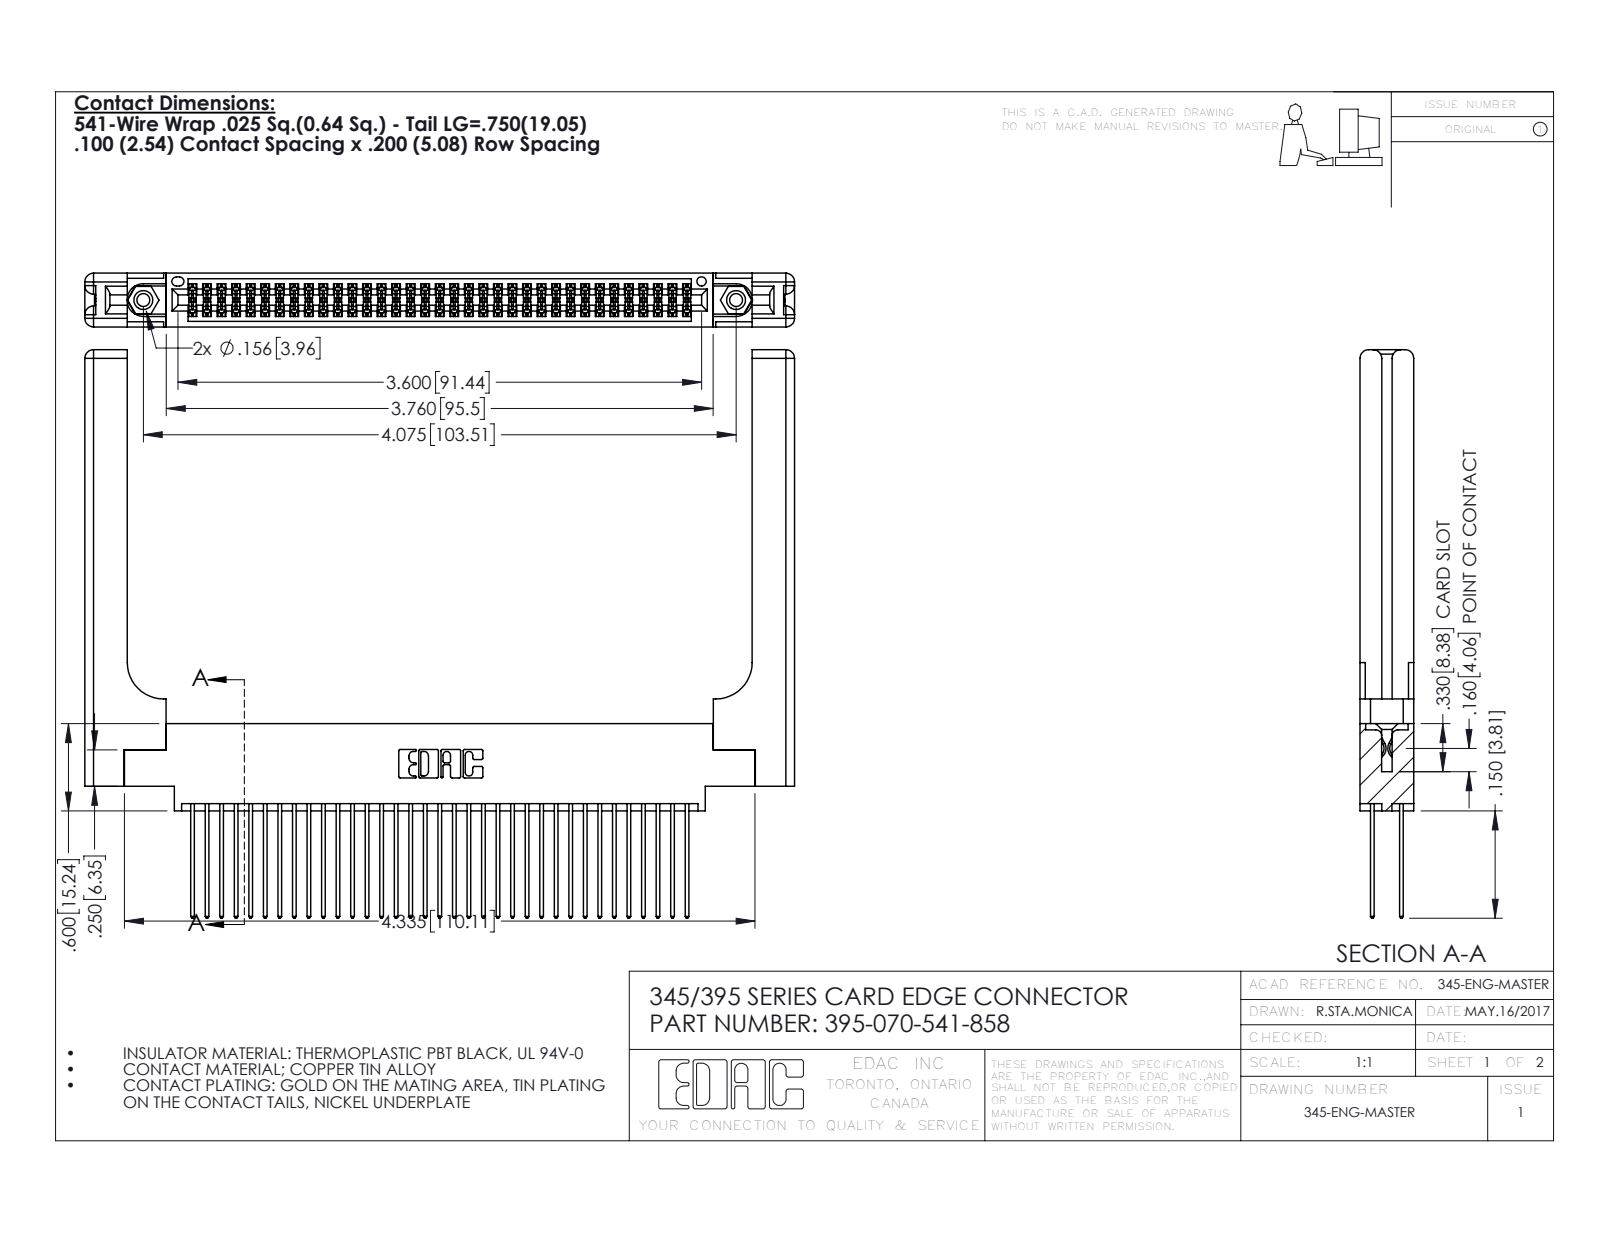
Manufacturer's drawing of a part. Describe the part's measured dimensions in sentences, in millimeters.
The part is named "345 Part_0.170 Offset - 0.156 Dia-TH; 345-250-001_345-250-001-102; 395-070-541-858; 345-220-058_345-220-058 (+1 more)". Its 3-D file was written by "SolidWorks 2016 (CONFIG_CONTROL_DESIGN)". It is 75 solids with 3886 faces: 2542 planar, 1284 cylindrical and 60 other. Overall it measures 123.9 by 99.2 by 9.4 millimeters. Its volume is 20 730 cubic millimeters and its surface area 25 080 square millimeters. Round holes: 2 of diameter 2.3, 2 of diameter 3.2, 2 of diameter 4, 1 of diameter 1.6. Round bosses or shafts: 2 of diameter 3.9. Partial cylindrical surfaces (rounded edges, fillets, slot ends): 105 of radius 0.2, 70 of radius 0.3, 22 of radius 0.3, 16 of radius 1.5, 6 of radius 0.2, 6 of radius 0.8, 3 of radius 0.7, 2 of radius 0.4. The main face-to-face distances are 1.8, 7.6, 9.4, 2.5, 6.9, 0.6, 5.1, 5.7, 4.4, 3.8. The hole center spacings are 6.9, 97.5, 103.5.
